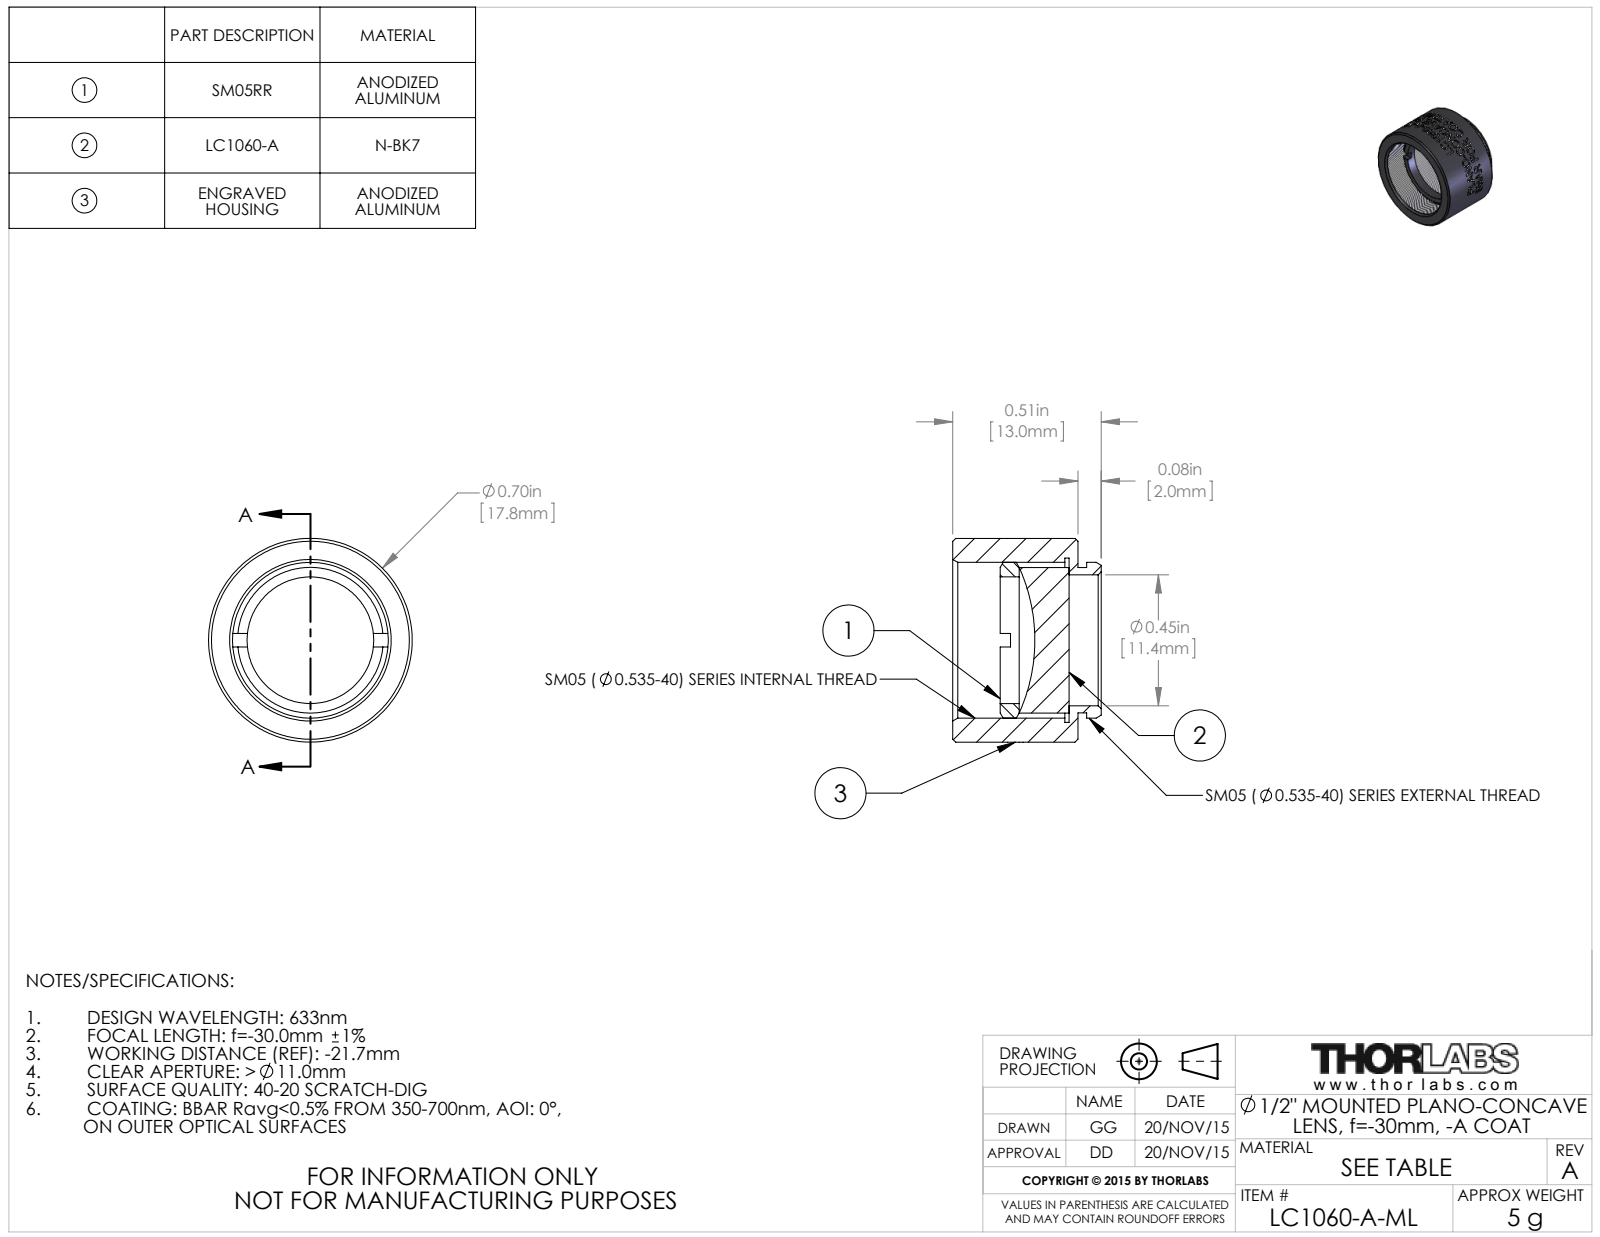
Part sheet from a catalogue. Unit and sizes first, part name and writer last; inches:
Units: inches
Overall size (bounding box): 0.7 × 0.7 × 0.51
Round holes (diameter × count): ⌀0.435 ×1, ⌀0.45 ×1, ⌀0.535 ×1, ⌀0.565 ×1
Round bosses / shafts (diameter × count): ⌀0.7 ×1, ⌀0.535 ×1, ⌀0.5 ×1, ⌀0.499 ×1
Main face-to-face distances: 0.03, 0.43, 0.4, 0.202, 0.172, 0.228, 0.267, 0.237, 0.065, 0.163
Volume: 0.107 in³ · Surface area: 3.407 in²
Bodies: 3 solids, 149 faces (16 planar, 116 cylindrical, 17 other)
Part name (STEP PRODUCT): TTN045248-E0W
STEP written by: SolidWorks 2014 (CONFIG_CONTROL_DESIGN)
